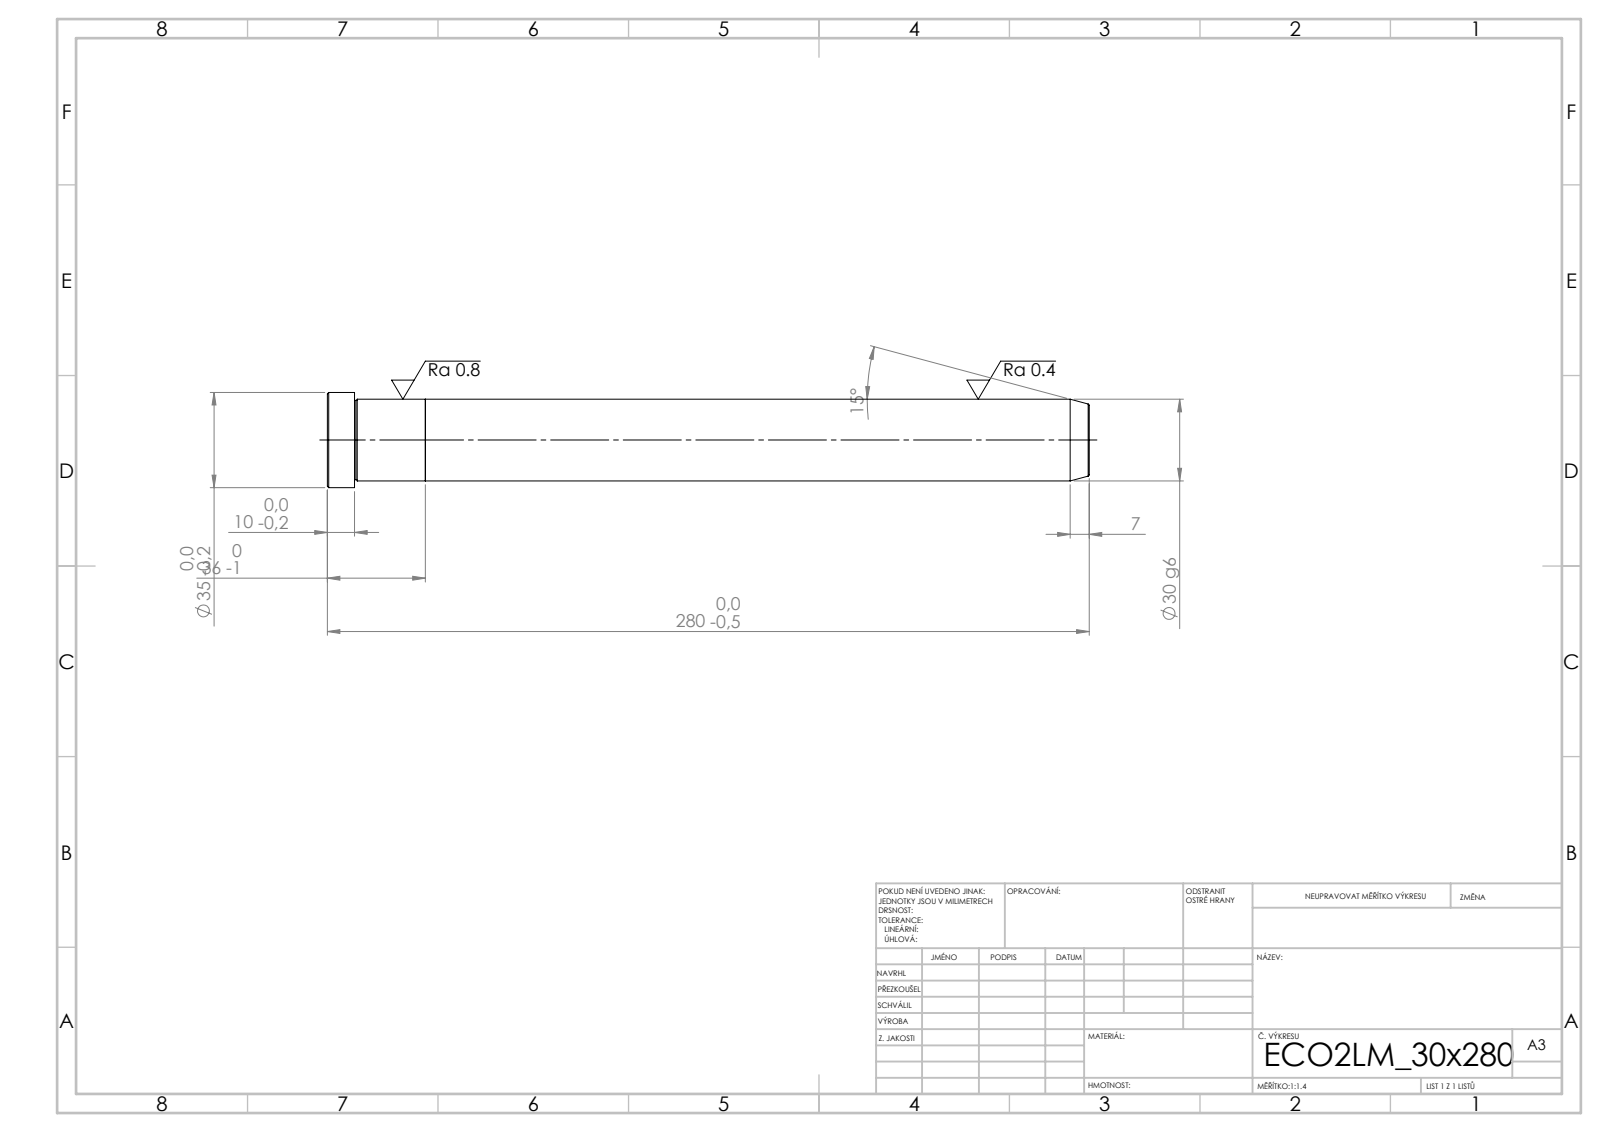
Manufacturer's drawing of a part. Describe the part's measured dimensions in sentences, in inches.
Its 3-D file was written by "SolidWorks 2019 (CONFIG_CONTROL_DESIGN)". It is 2 solids with 21 faces: 5 planar, 6 cylindrical and 10 other. Overall it measures 11.024 by 1.378 by 1.378 inches. Its volume is 12.19 cubic inches and its surface area 46.05 square inches. Round bosses or shafts: 1 of diameter 1.378, 1 of diameter 1.181. The main face-to-face distances are 1.417, 9.606, 11.024, 10.63, 1.024, 0.394.
